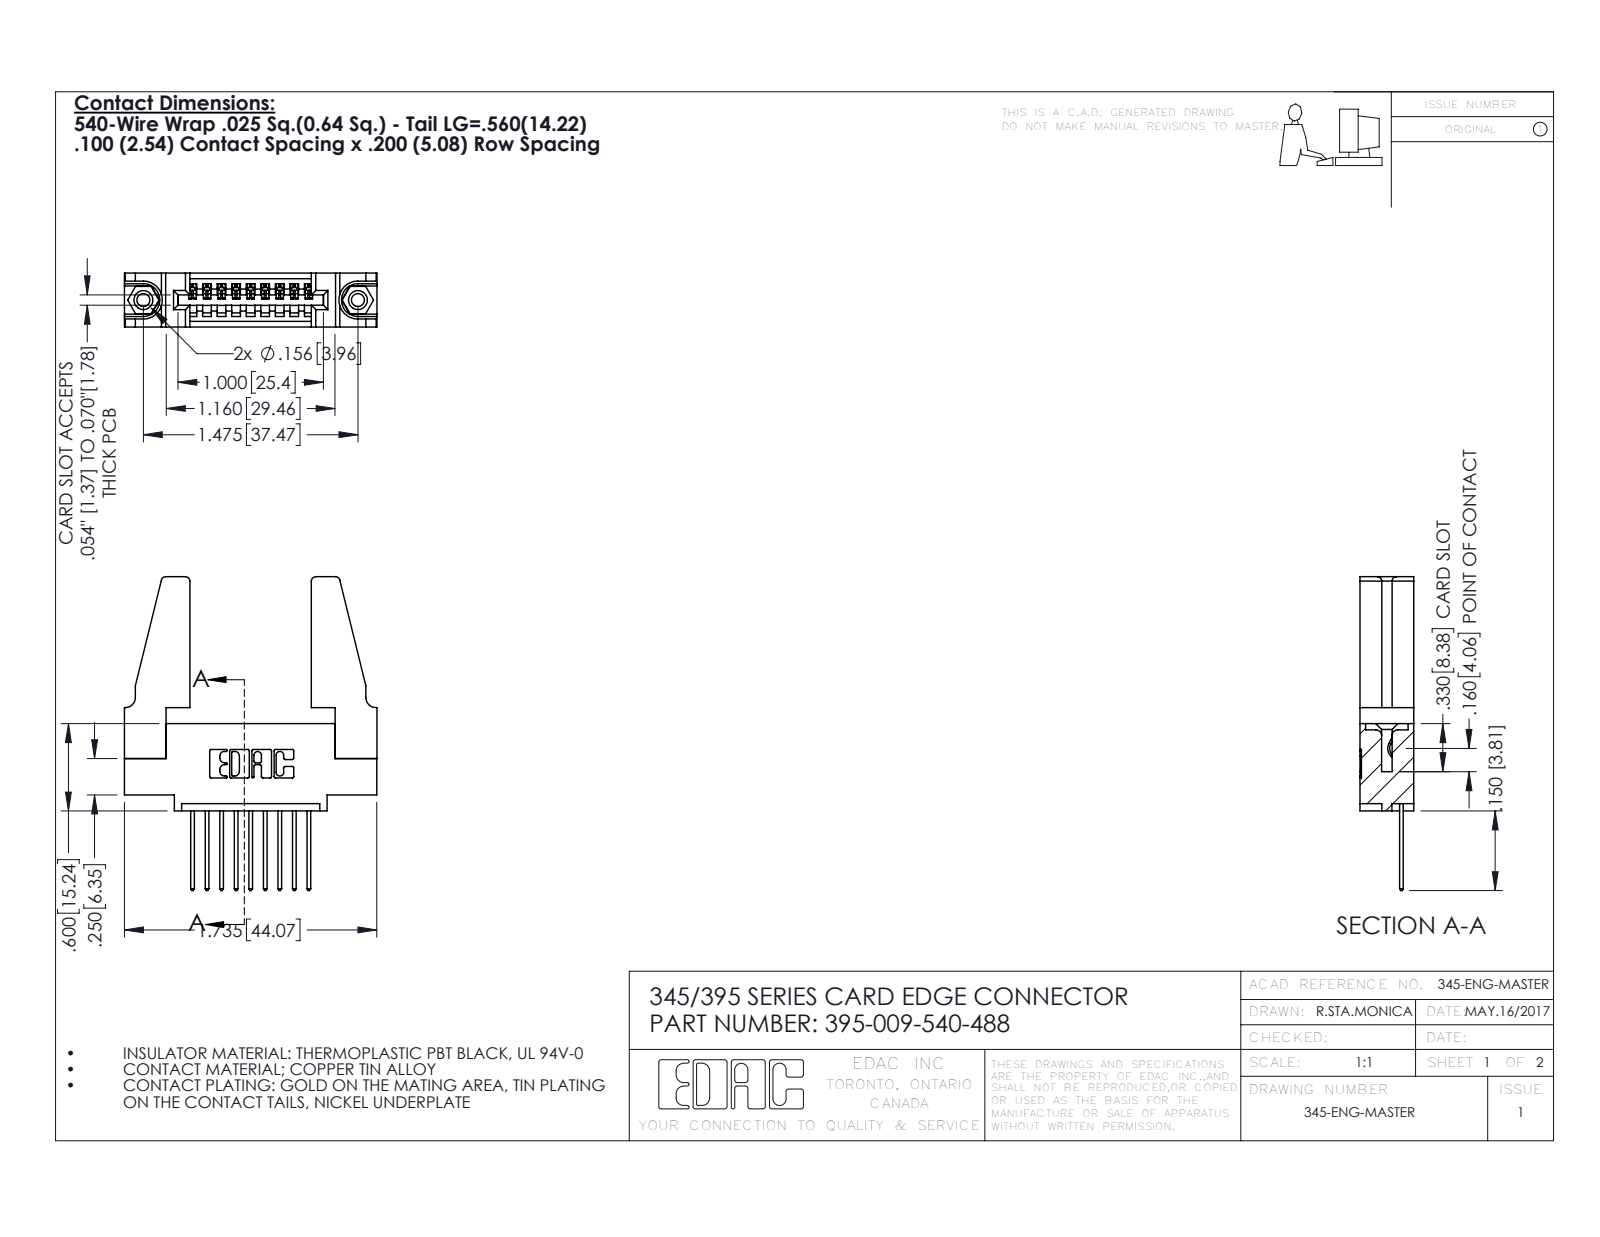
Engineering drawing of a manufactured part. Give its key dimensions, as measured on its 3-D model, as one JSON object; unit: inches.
{"part_name": "345 Part_0.110 Offset - 0.156 Dia-TH; 345-220-078_345-220-088; 395-009-540-488; 345-292-001_345-293-140 (+1 more)", "step_written_by": "SolidWorks 2016 (CONFIG_CONTROL_DESIGN)", "units": "inches", "bodies": {"solids": 14, "faces": 776, "planar": 516, "cylindrical": 244, "other": 16}, "overall_size": [2.157, 1.736, 0.37], "volume_in3": 0.434, "surface_area_in2": 12.36, "round_holes": [[0.089, 2], [0.125, 2], [0.156, 2], [0.064, 1]], "round_bosses_or_shafts": [[0.155, 2]], "partial_cylinders_radius": [[0.01, 22], [0.006, 18], [0.01, 18], [0.03, 8], [0.007, 6], [0.031, 6], [0.026, 3], [0.031, 2]], "face_to_face_distances": [0.37, 0.072, 0.298, 0.2, 0.098, 0.272, 0.025, 0.15, 0.148, 0.225], "hole_center_spacings": [0.27, 1.244, 1.475]}
